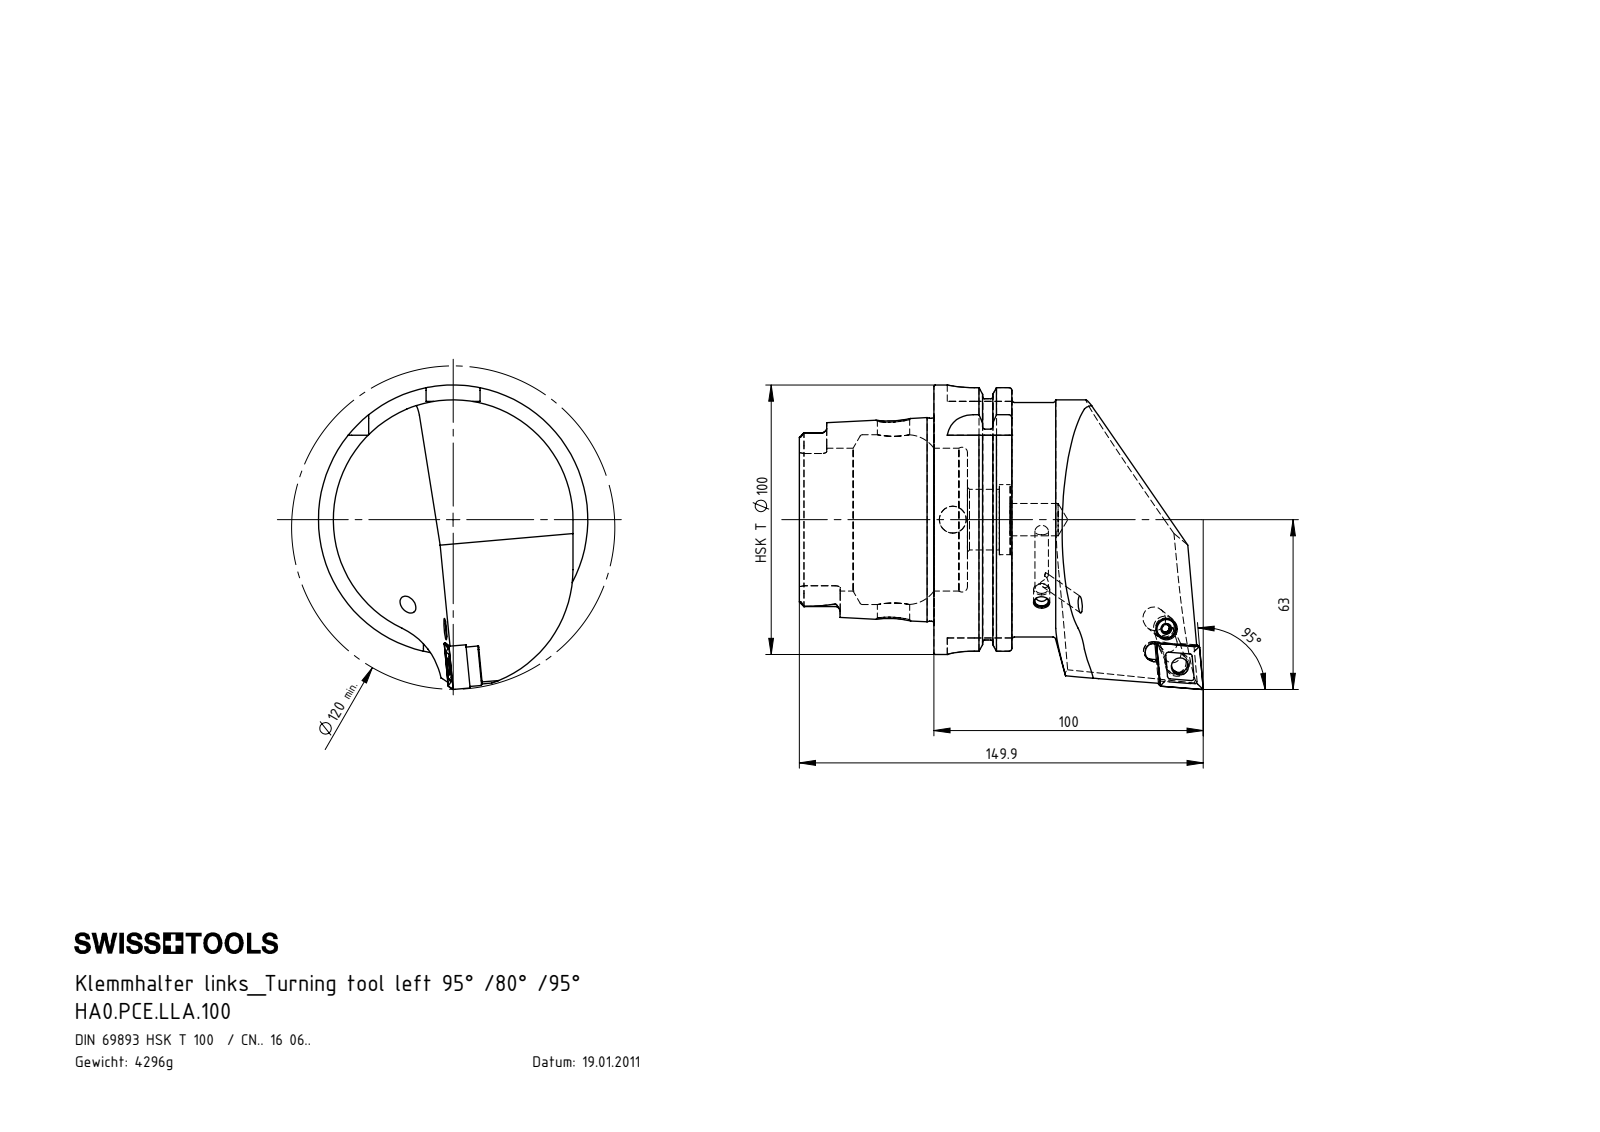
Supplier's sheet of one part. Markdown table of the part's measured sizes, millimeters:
| quantity | value |
| --- | --- |
| part name | HA0-PCE.LLA.100; WCE-ER3.101.000_A; WCE-ER4.101.020_A; KVT_MB_600_060 (+3 more) |
| STEP written by | SolidWorks 2012 (CONFIG_CONTROL_DESIGN) |
| units | millimeters |
| bodies | 7 solids, 364 faces (114 planar, 102 cylindrical, 148 other) |
| overall size | 149.9 × 113 × 100 |
| volume | 555 395 mm³ |
| surface area | 72 945 mm² |
| round holes (diameter × count) | 5 × 2, 12 × 2, 6.35 × 1, 7 × 1, 8.05 × 1, 8.4 × 1, 10 × 1, 22.5 × 1, 26 × 1, 53 × 1, 63 × 1 |
| round bosses / shafts (diameter × count) | 6 × 2, 100 × 1, 91.95 × 1, 87 × 1, 75.26 × 1, 8 × 1, 7.9 × 1, 6.4 × 1 |
| partial cylindrical surfaces (radius × count) | 1.9 × 6, 0.4 × 4, 1.5 × 4, 10 × 4, 3.5 × 3, 4.83 × 2, 4.88 × 2, 3.1 × 1 |
| main face-to-face distances | 12.45, 28.95, 16.5, 49.9, 62.35, 78.85, 87.8, 78.2, 28.3, 15.85 |
| hole center spacings | 14.75, 14.99 |
